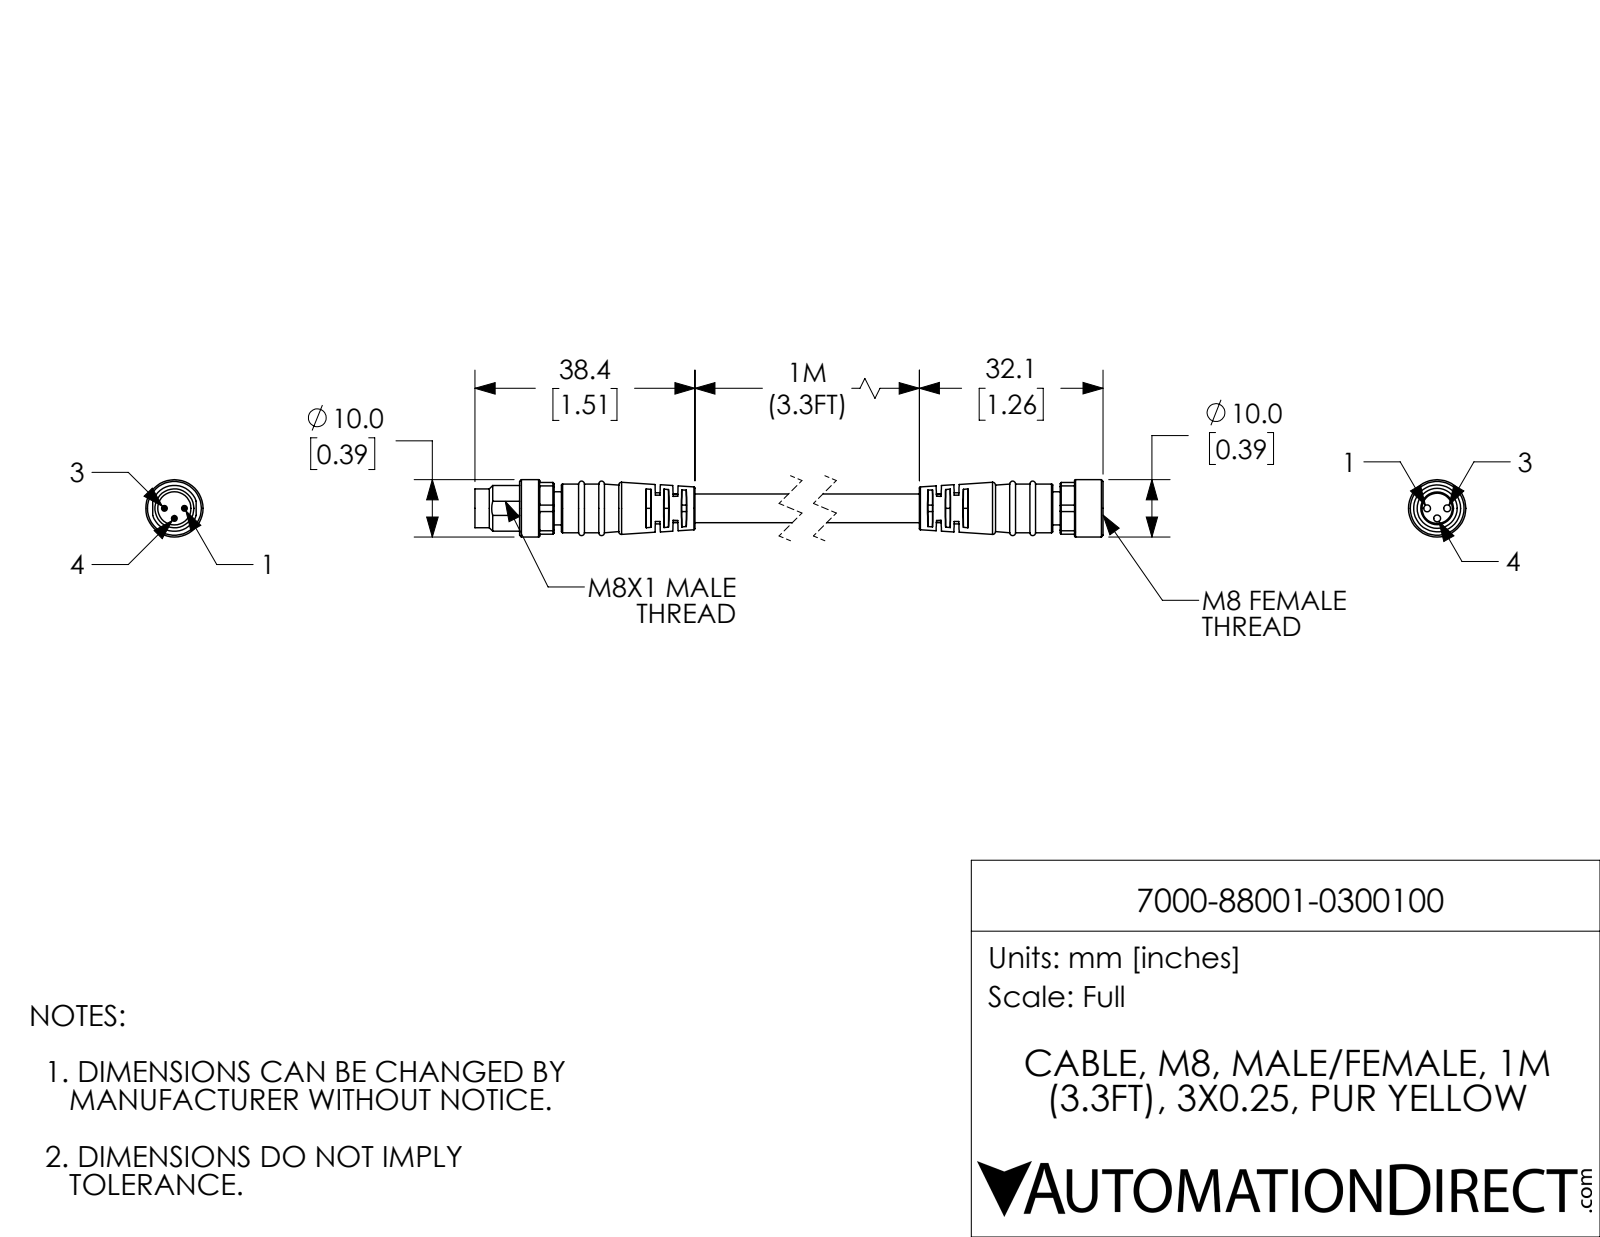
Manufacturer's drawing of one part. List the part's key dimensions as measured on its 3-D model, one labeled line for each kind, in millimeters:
Part name (STEP PRODUCT): 7000-88001-0300100_MALE; 7000-88001-0300100_FEMALE; 7000-88001-0300100
STEP written by: SolidWorks 2021 (CONFIG_CONTROL_DESIGN)
Units: millimetres
Bodies: 2 solids, 273 faces (138 planar, 66 cylindrical, 69 other)
Overall size (bounding box): 122.5 × 10 × 10
Volume: 4 460 mm³ · Surface area: 3 618 mm²
Round holes (diameter × count): ⌀1.2 ×3, ⌀7 ×1
Round bosses / shafts (diameter × count): ⌀1 ×3, ⌀10 ×1, ⌀8.5 ×1, ⌀8 ×1, ⌀6.8 ×1, ⌀5.8 ×1, ⌀5.7 ×1, ⌀5 ×1
Partial cylindrical surfaces — rounded edges, fillets, slot ends (radius × count): R4.9 ×1
Main face-to-face distances: 3.1, 3.1, 0.6, 108.7, 3.7, 9, 1.3, 99.9, 0.7, 8.8
Hole centre spacings: 1.8, 2.5, 3.5
